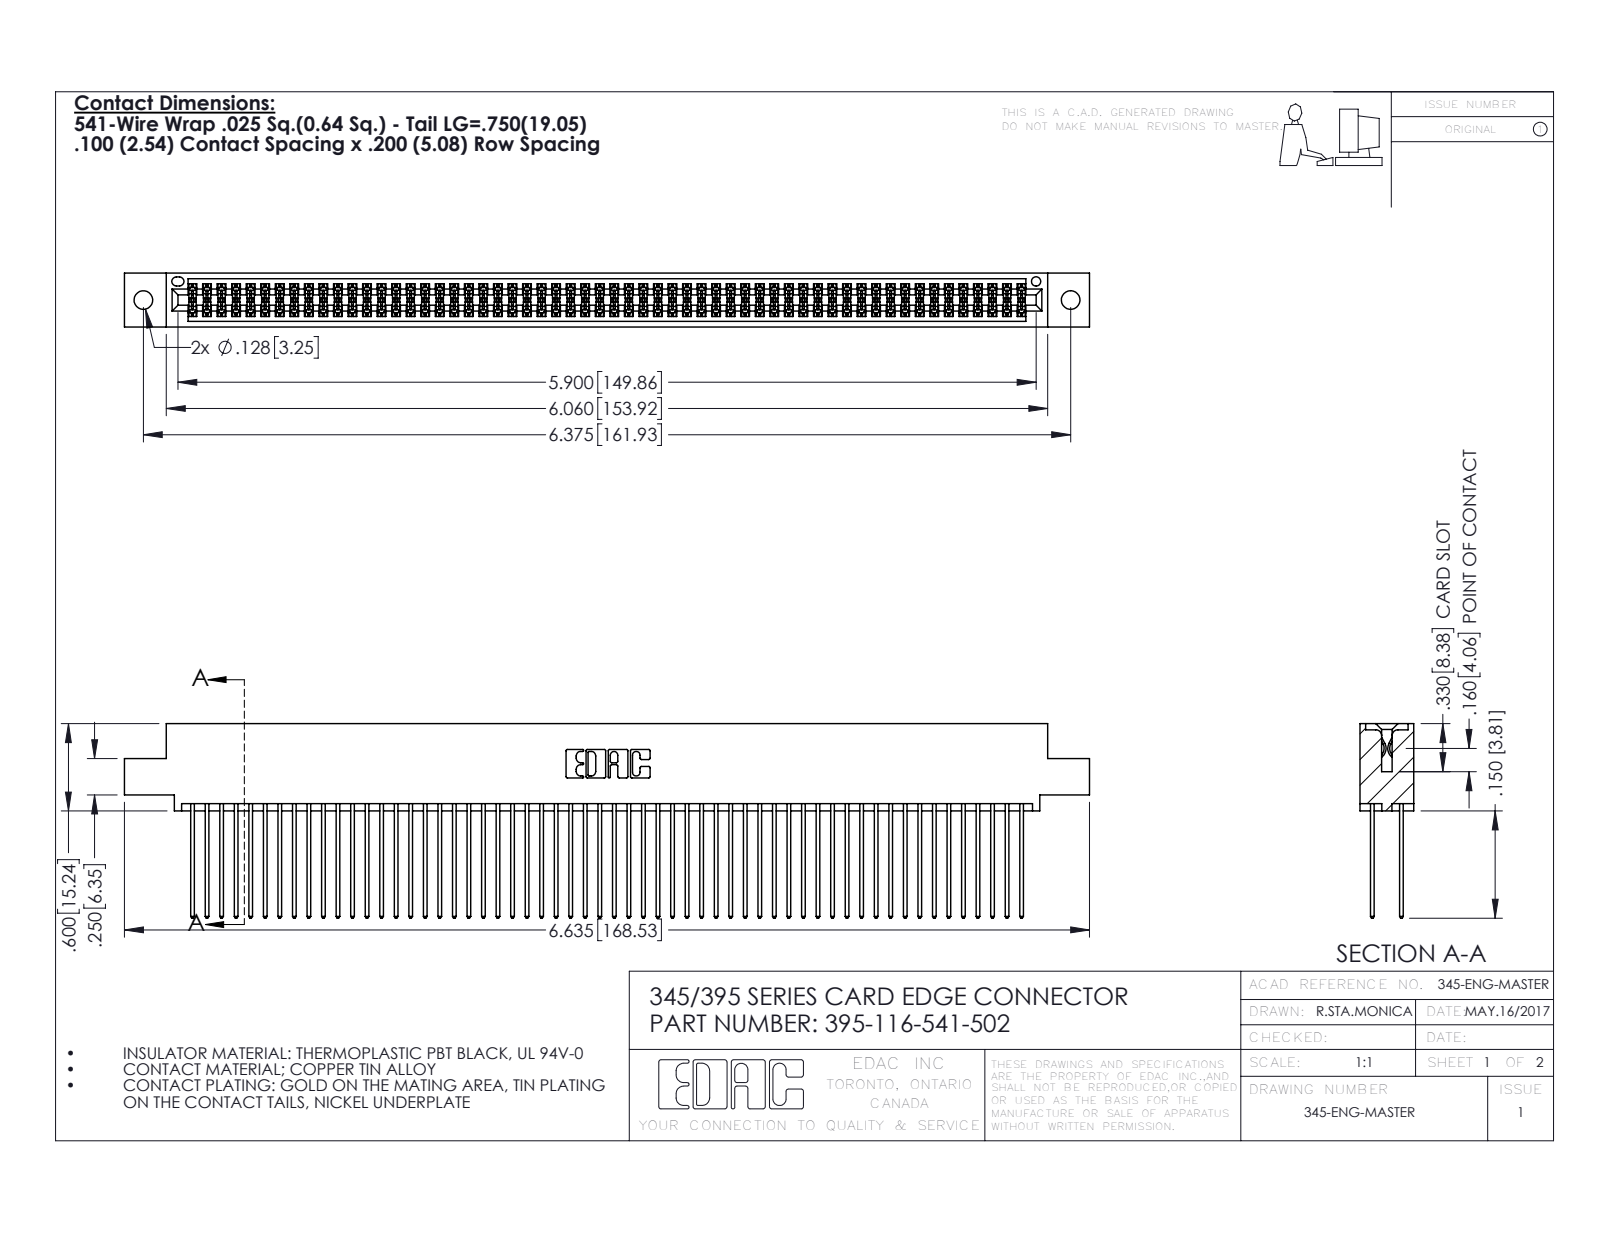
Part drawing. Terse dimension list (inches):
name: 345 Part_0.110 Offset - 0.128 Dia; 395-116-541-502; 345-292-001_345-293-141
written by: SolidWorks 2016 (CONFIG_CONTROL_DESIGN)
unit: in
bodies: 117 solids, 5930 faces (3912 planar, 2018 cylindrical, 0 other)
size: 6.635 × 1.337 × 0.37
volume: 1.042 in³; area: 44.17 in²
holes: 2× ⌀0.128, 1× ⌀0.064
rounds: 174× R0.006, 116× R0.01, 22× R0.01, 6× R0.007, 6× R0.031, 3× R0.026, 2× R0.014, 2× R0.019
face distances: 0.298, 0.072, 0.2, 0.098, 0.272, 0.025, 0.225, 0.37, 0.175, 0.149
hole spacings: 0.27, 6.139, 6.375
